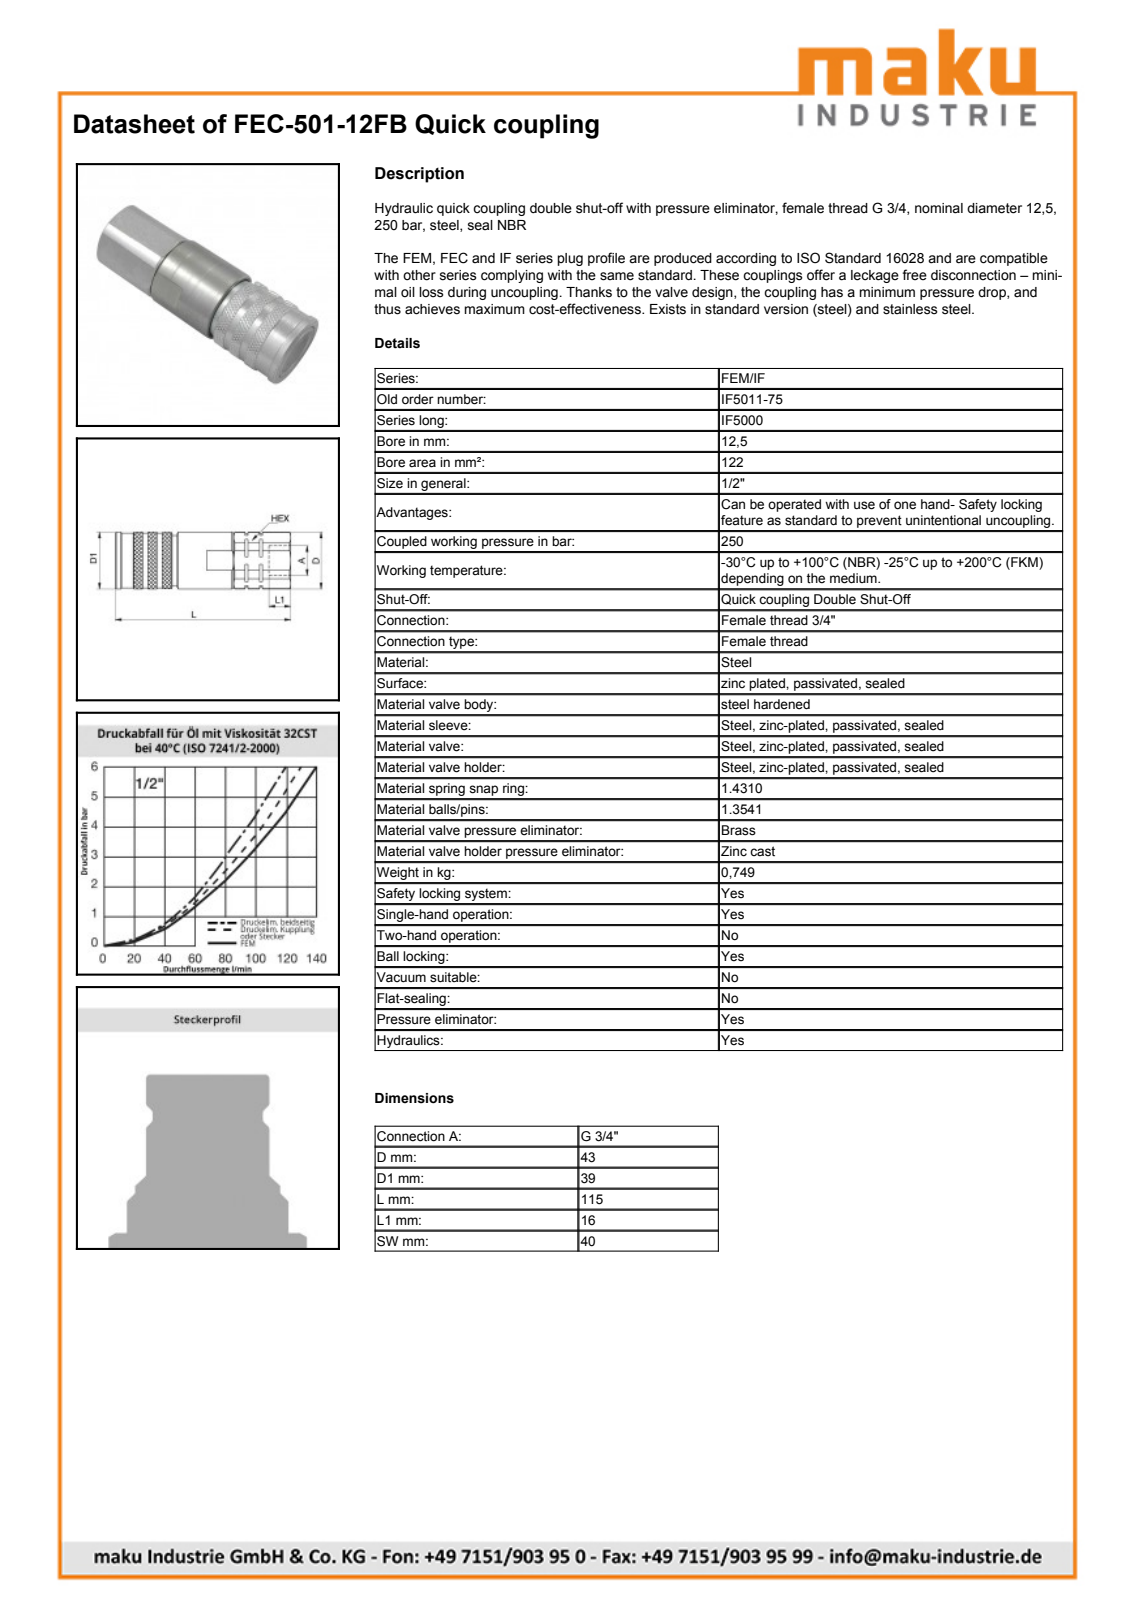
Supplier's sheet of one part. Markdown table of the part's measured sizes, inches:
| quantity | value |
| --- | --- |
| part name | FEC-501-12FB |
| STEP written by | SolidWorks 2009 (AUTOMOTIVE_DESIGN) |
| units | inches |
| bodies | 1 solid, 127 faces (38 planar, 51 cylindrical, 38 other) |
| overall size | 4.512 × 1.693 × 1.575 |
| volume | 7.796 in³ |
| surface area | 32.04 in² |
| round holes (diameter × count) | 0.079 × 1, 0.62 × 1, 0.95 × 1, 0.972 × 1, 1.209 × 1, 1.35 × 1, 1.354 × 1 |
| round bosses / shafts (diameter × count) | 1.535 × 1, 1.496 × 1, 1.445 × 1, 1.396 × 1, 1.339 × 1, 1.181 × 1, 0.965 × 1, 0.612 × 1 |
| partial cylindrical surfaces (radius × count) | 0.02 × 2, 0.61 × 1, 0.846 × 1 |
| main face-to-face distances | 1.575, 0.079, 1.496, 4.512, 0.698, 3.814, 4.5, 3.802, 1.417, 1.378 |
